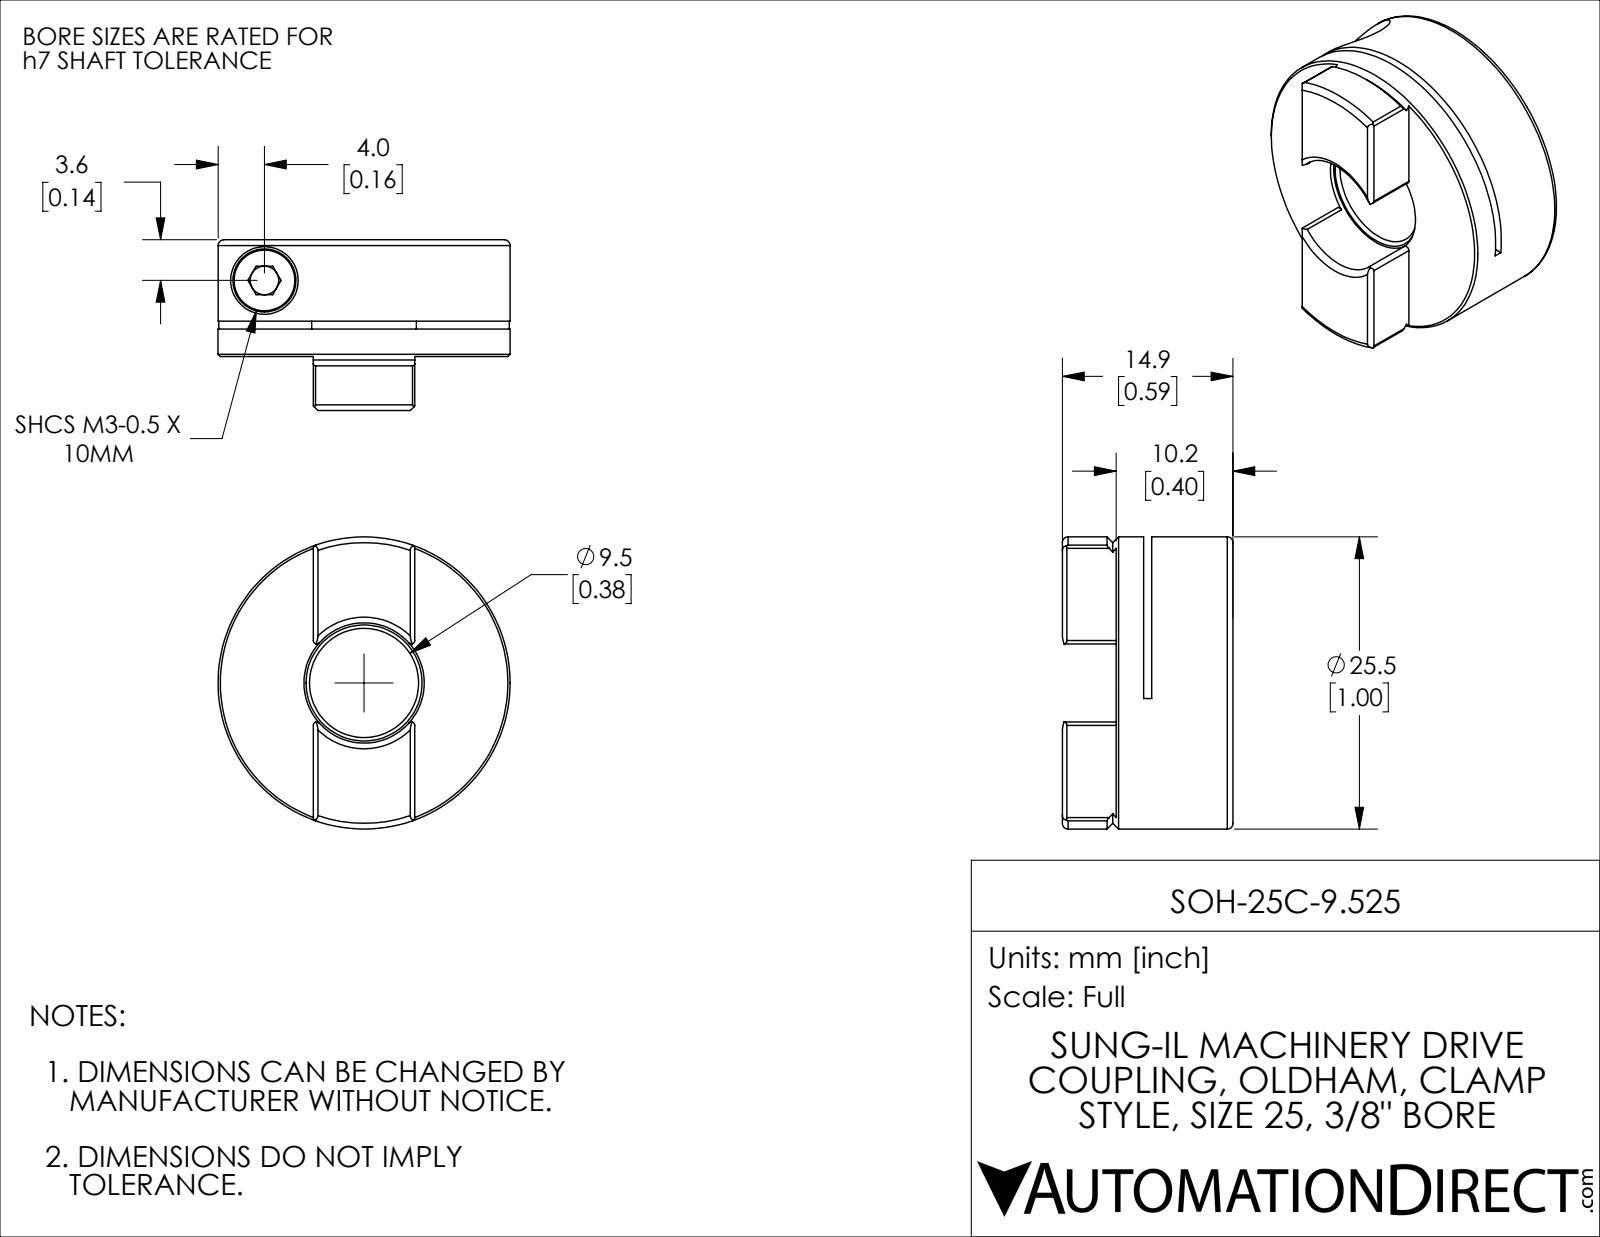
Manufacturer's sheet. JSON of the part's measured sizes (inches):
{"part_name": "SOH-25C-9.525", "step_written_by": "SolidWorks 2021 (CONFIG_CONTROL_DESIGN)", "units": "inches", "bodies": {"solids": 2, "faces": 98, "planar": 39, "cylindrical": 33, "other": 26}, "overall_size": [1.004, 1.004, 0.587], "volume_in3": 0.292, "surface_area_in2": 5.016, "round_holes": [[0.098, 1], [0.13, 1], [0.232, 1], [0.375, 1], [0.413, 1]], "round_bosses_or_shafts": [[1.004, 1], [0.217, 1], [0.118, 1]], "partial_cylinders_radius": [[0.012, 8], [0.886, 1]], "face_to_face_distances": [0.307, 0.28, 0.402, 0.094, 0.028, 0.122, 0.587, 0.185, 0.349, 0.031]}
